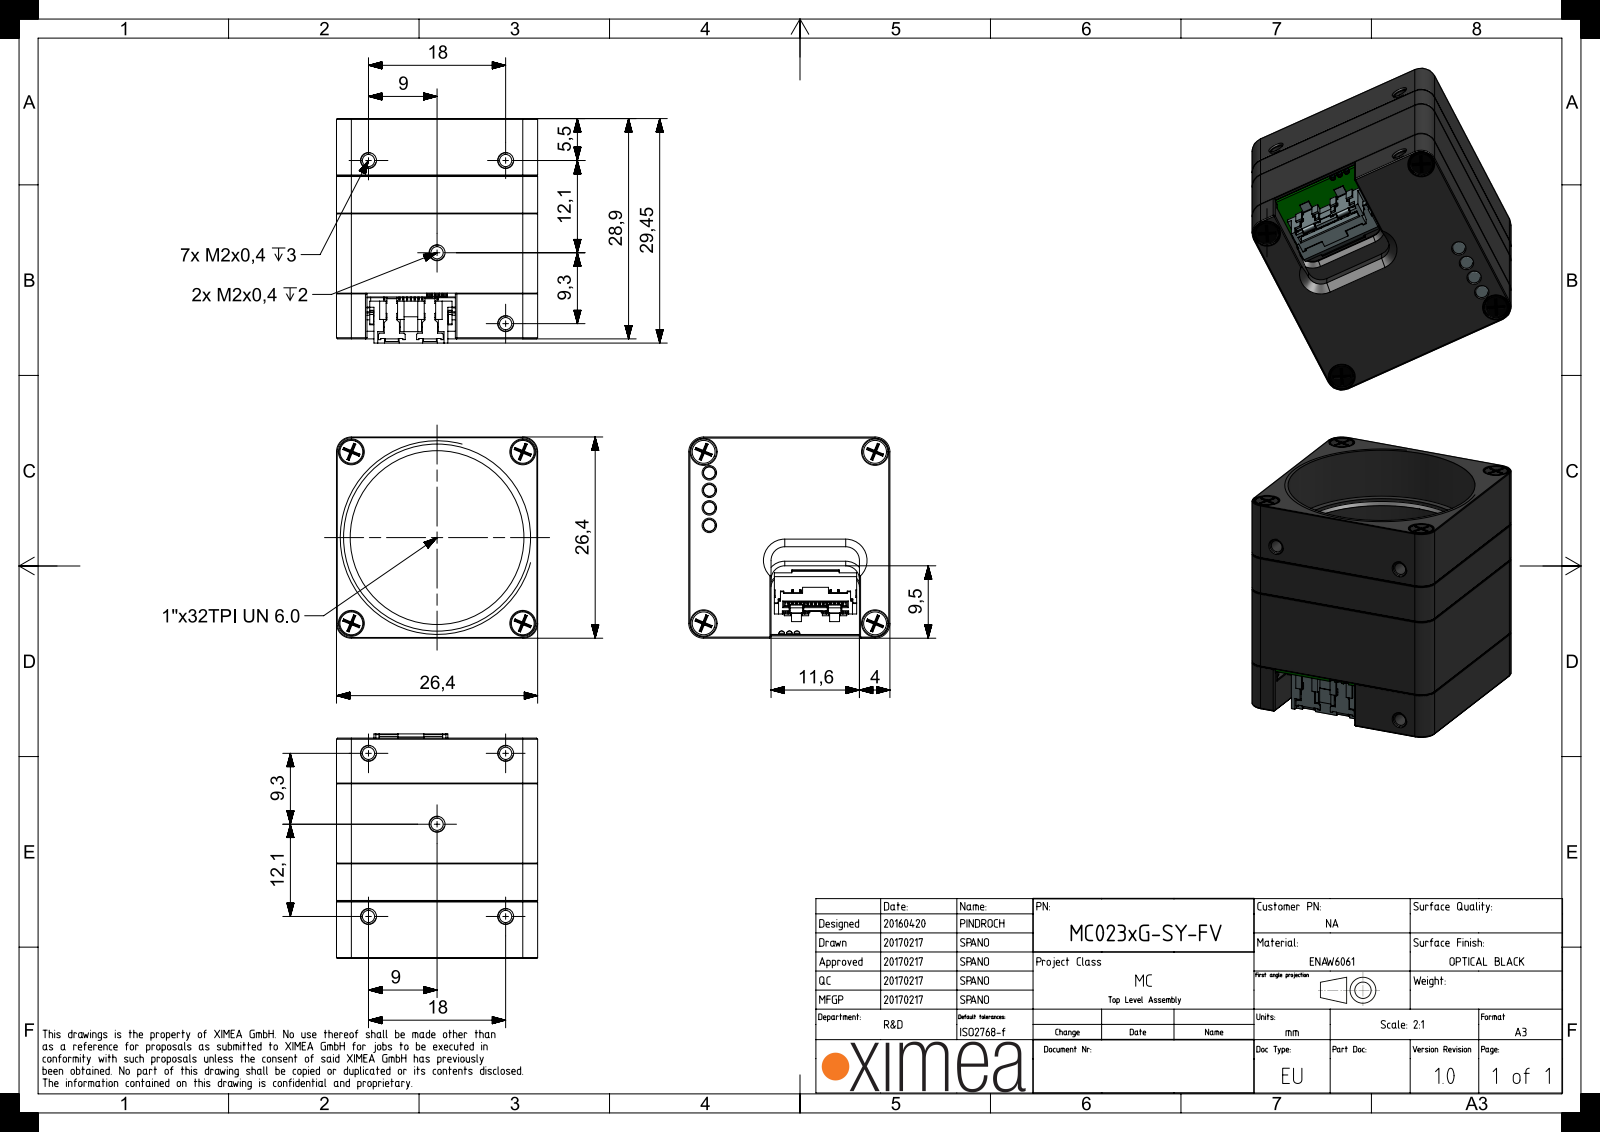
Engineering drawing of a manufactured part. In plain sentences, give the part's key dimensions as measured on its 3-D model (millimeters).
The part is named "SROB-M2x14-CUST; MECH-MQ-FRONT; MECH-MQ-CS-C; MC_REAR_THERMAL_PAD (+8 more)". Its 3-D file was written by "SIEMENS PLM Software NX 11.0 (AUTOMOTIVE_DESIGN)". It is 31 solids with 5640 faces: 4000 planar, 1376 cylindrical and 264 other. Overall it measures 29.4 by 26.4 by 26.4 millimeters. Its volume is 9 900 cubic millimeters and its surface area 17 270 square millimeters. Round holes: 13 of diameter 1.6, 4 of diameter 1, 4 of diameter 1.8, 4 of diameter 2, 4 of diameter 2.1, 4 of diameter 3, 4 of diameter 3.2, 4 of diameter 3.4, 2 of diameter 1.1, 2 of diameter 1.4, 2 of diameter 1.9, 1 of diameter 4. Round bosses or shafts: 4 of diameter 1.9, 4 of diameter 1.6, 4 of diameter 0.8, 2 of diameter 2.6, 1 of diameter 25, 1 of diameter 21.6. Partial cylindrical surfaces (rounded edges, fillets, slot ends): 26 of radius 1, 16 of radius 1.3, 14 of radius 0.1, 12 of radius 1.5, 8 of radius 0.2, 8 of radius 0.3, 4 of radius 0.2, 4 of radius 0.2. The main face-to-face distances are 1, 3.6, 26.4, 6.9, 4.8, 6.8, 10.5, 9.4, 5.8, 11.5. The hole center spacings are 3.8, 12.9, 15.9, 18.8, 22.1, 22.5, 28.7, 2.3.
